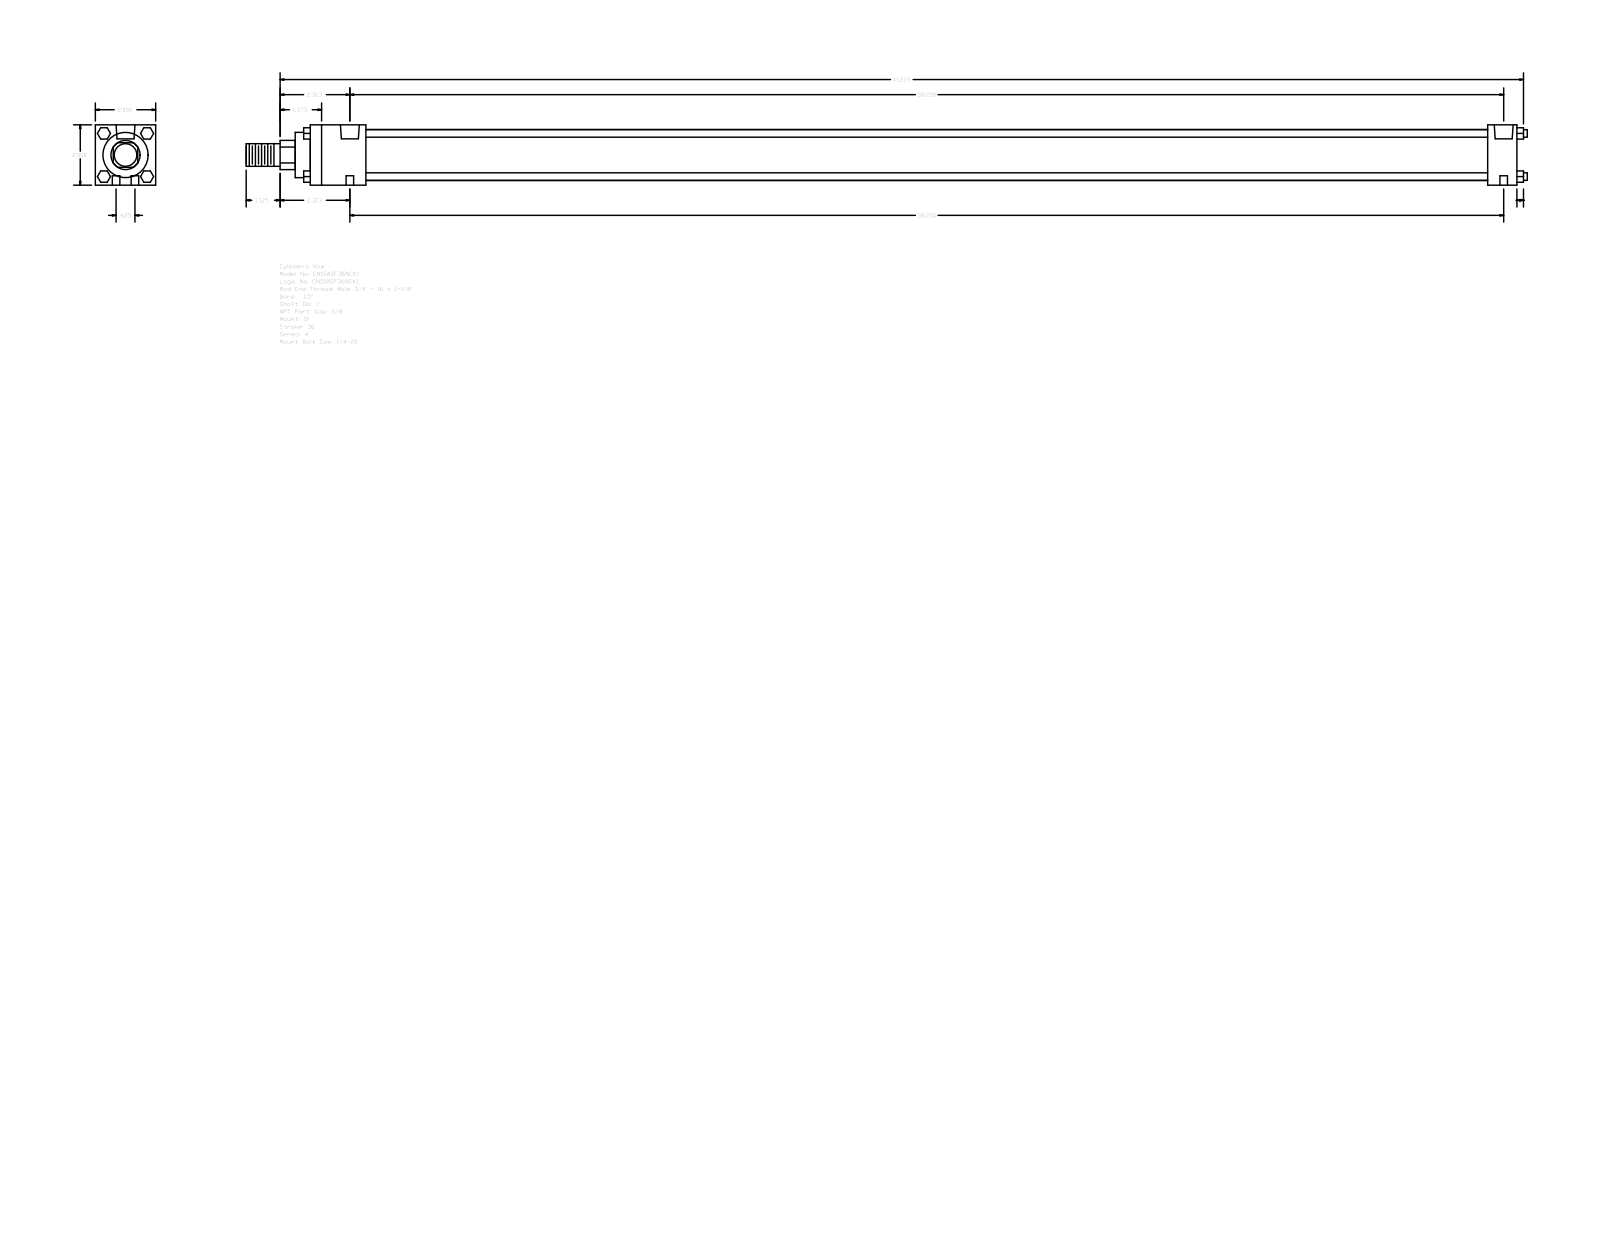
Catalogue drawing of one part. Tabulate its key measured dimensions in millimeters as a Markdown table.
| quantity | value |
| --- | --- |
| part name | A_SF__0150_1 |
| STEP written by | GSSL Pune (CONFIG_CONTROL_DESIGN) |
| units | millimeters |
| bodies | 0 solids, 124 faces (94 planar, 30 cylindrical, 0 other) |
| overall size | 1078.71 × 50.8 × 50.8 |
| round holes (diameter × count) | 6.35 × 4, 5.56 × 2, 15.93 × 2 |
| round bosses / shafts (diameter × count) | 6.35 × 4, 42.93 × 1, 38.1 × 1, 25.4 × 1, 19.05 × 1 |
| partial cylindrical surfaces (radius × count) | 12.29 × 1 |
| main face-to-face distances | 50.8, 1016, 46.83, 991.39, 944.56, 969.17, 24.61, 12.7, 59.53, 1004.09 |
| hole center spacings | 7.94, 971.58, 971.55, 15.88, 971.68, 963.61 |
